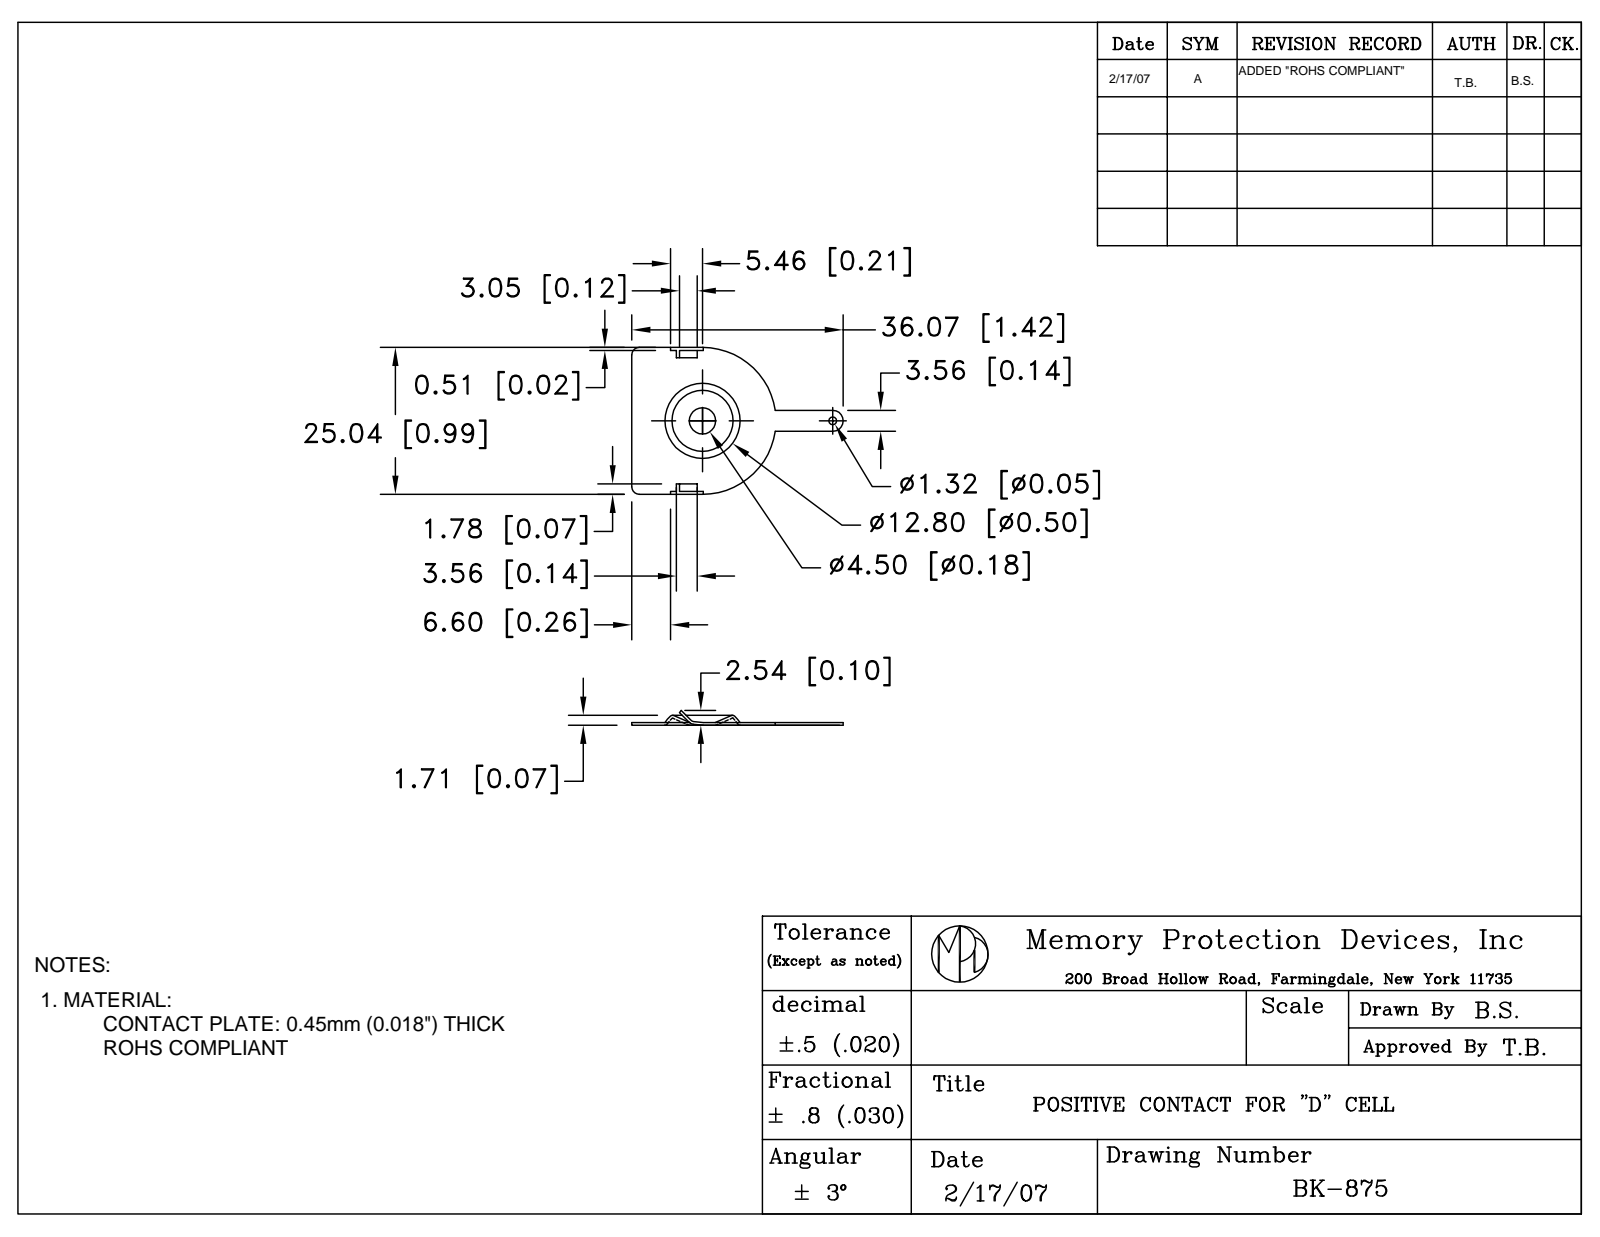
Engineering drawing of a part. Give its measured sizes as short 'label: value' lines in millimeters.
name: BK-875
written by: SolidWorks 2017 (AUTOMOTIVE_DESIGN)
unit: mm
bodies: 1 solid, 60 faces (33 planar, 11 cylindrical, 16 other)
size: 36.07 × 25.04 × 2.54
volume: 274 mm³; area: 1 279 mm²
holes: 1× ⌀1.32
rounds: 2× R1, 1× R0.5, 1× R0.95, 1× R1.78, 1× R12.52
face distances: 0.45, 1.26, 1.71, 0.81, 10.23, 13.79, 0.51, 10.74, 14.3, 24.53
